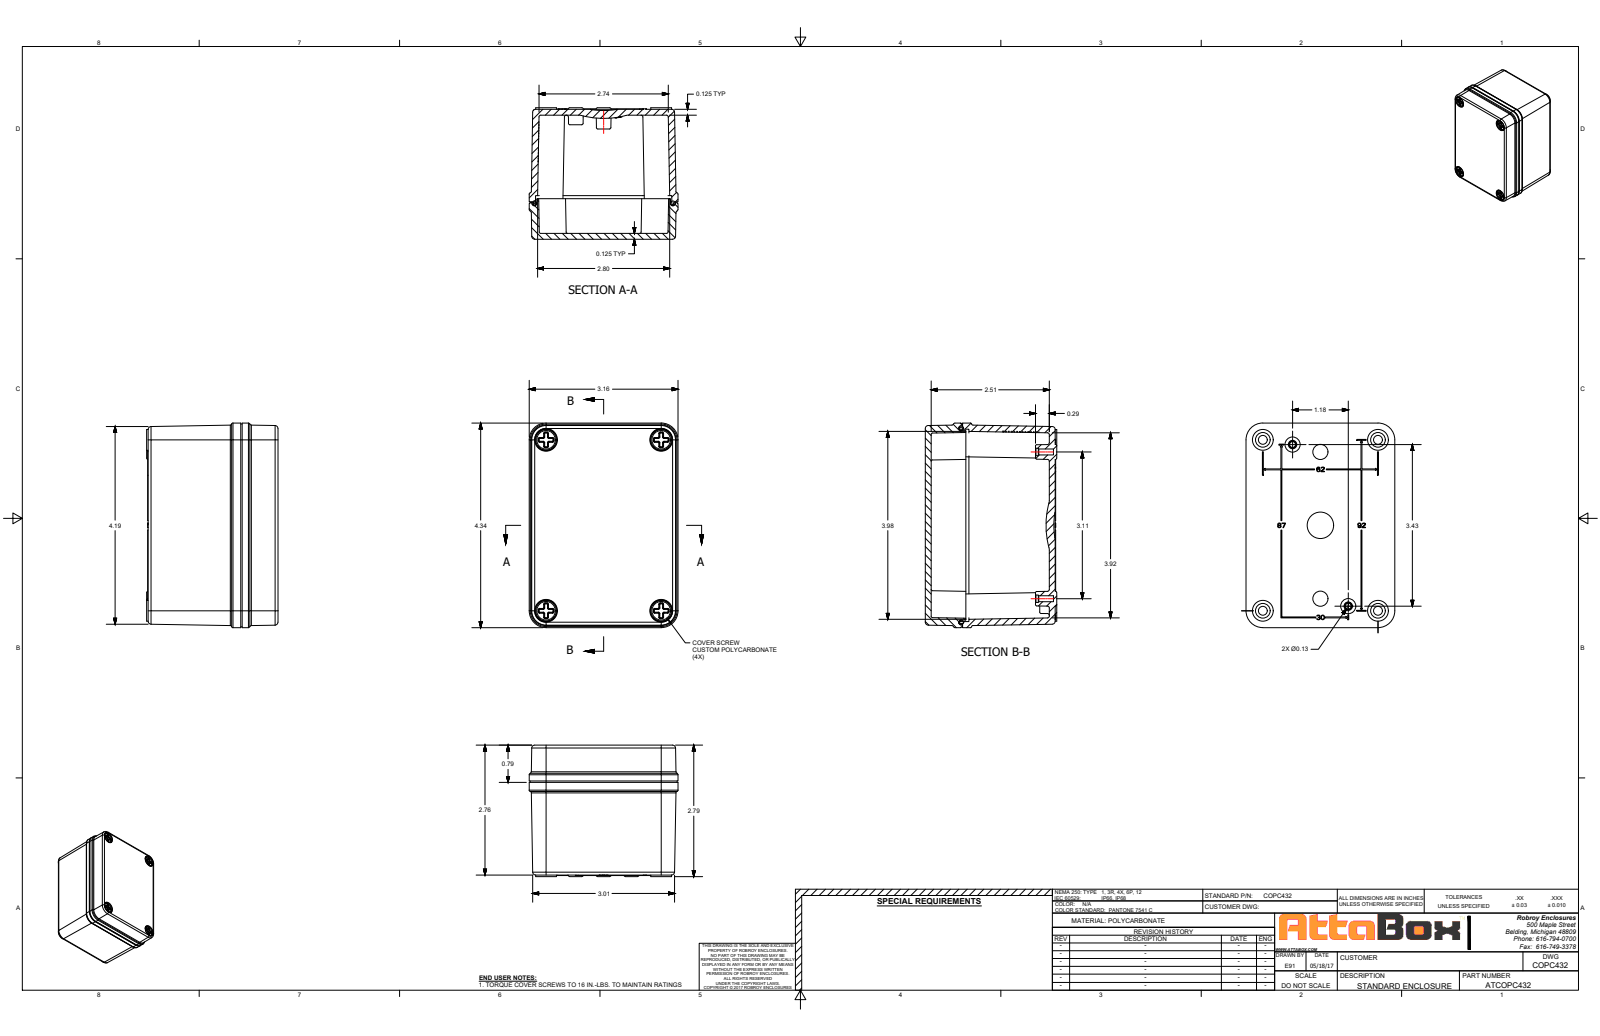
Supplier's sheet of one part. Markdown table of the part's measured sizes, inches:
| quantity | value |
| --- | --- |
| part name | COPC432 |
| STEP written by | SolidWorks 2018 (AUTOMOTIVE_DESIGN) |
| units | inches |
| bodies | 7 solids, 1098 faces (253 planar, 472 cylindrical, 373 other) |
| overall size | 4.336 × 3.155 × 2.787 |
| volume | 10.09 in³ |
| surface area | 153.4 in² |
| round holes (diameter × count) | 0.1 × 6, 0.187 × 4, 0.312 × 4, 0.46 × 4, 0.126 × 2, 0.146 × 2, 0.157 × 2, 0.495 × 2, 0.495 × 2 |
| round bosses / shafts (diameter × count) | 0.44 × 4, 0.433 × 4, 0.276 × 4, 0.309 × 2, 0.306 × 2, 0.1 × 2 |
| partial cylindrical surfaces (radius × count) | 0.02 × 48, 0.01 × 32, 0.03 × 16, 0.02 × 15, 0.015 × 12, 0.033 × 8, 0.07 × 8, 0.12 × 8 |
| main face-to-face distances | 2.755, 0.125, 2.63, 2.63, 2.505, 0.125, 0.161, 2.8, 0.178, 1.965 |
| hole center spacings | 1.247, 3.581, 0.57, 0.611, 0.637, 1.814, 2.441, 3.32 |
